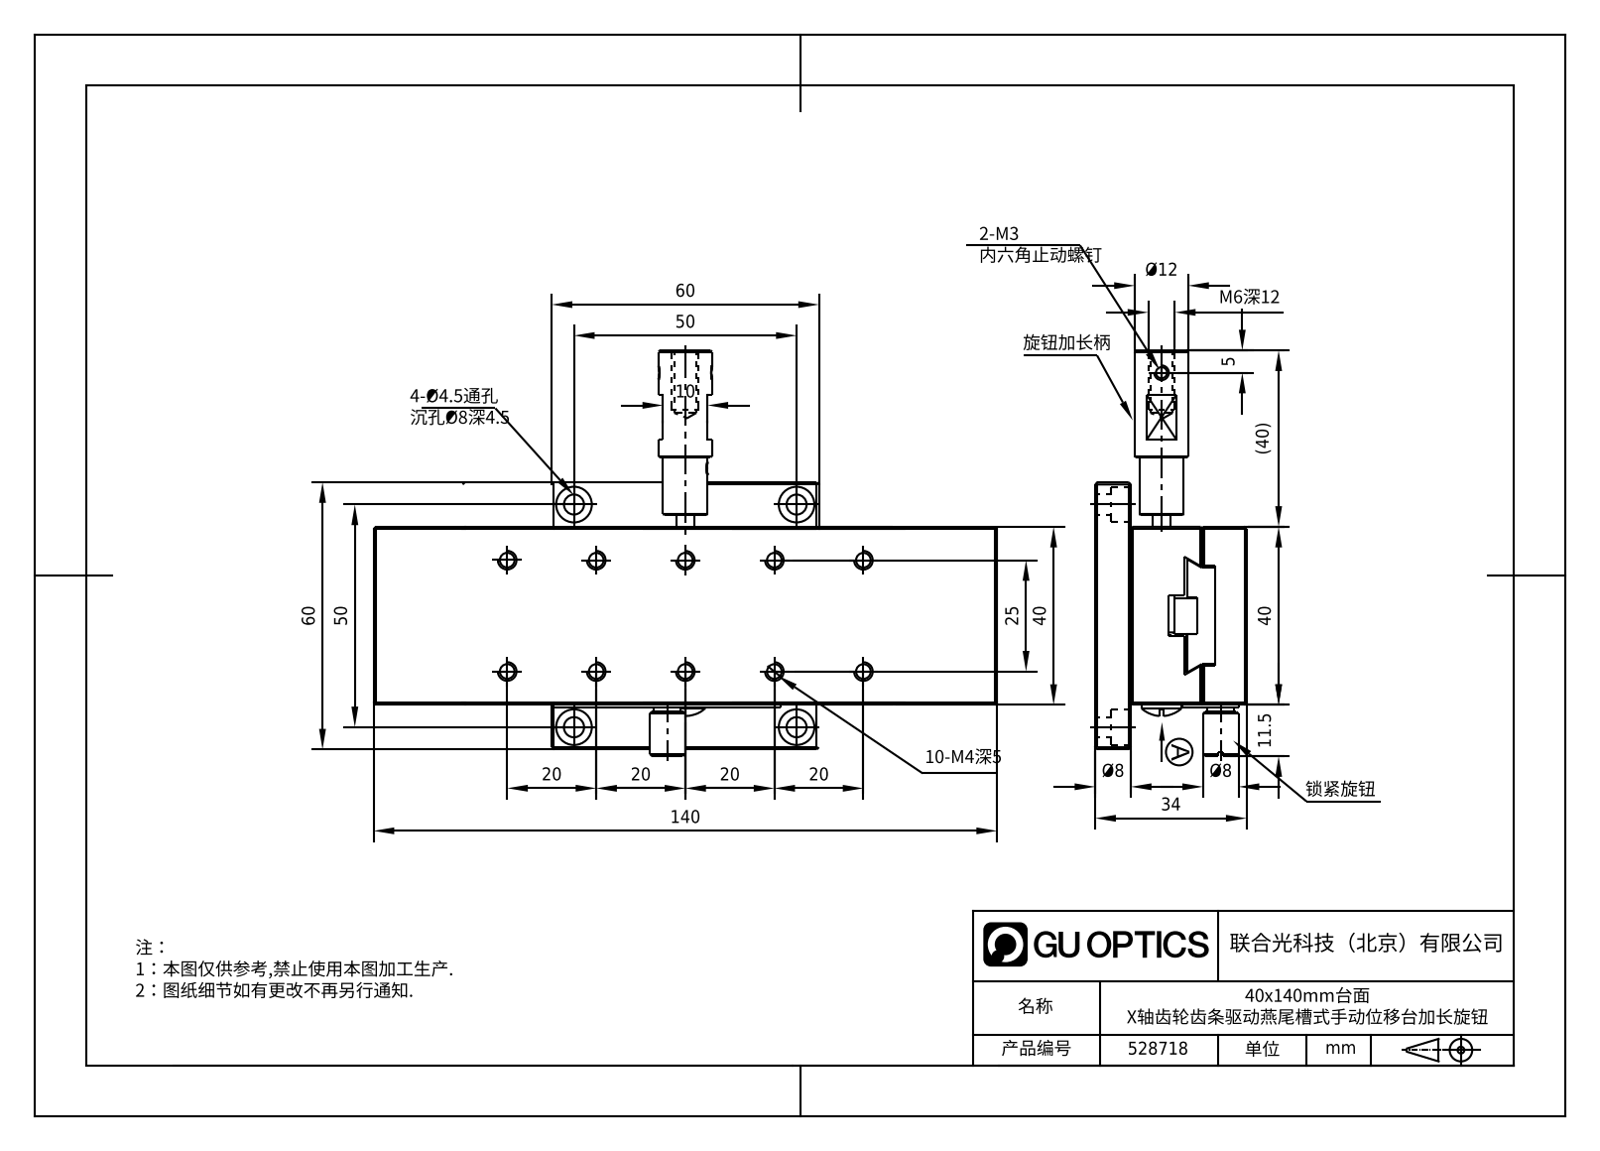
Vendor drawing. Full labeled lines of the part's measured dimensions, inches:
Part name (STEP PRODUCT): 528718
STEP written by: SolidWorks 2020 (CONFIG_CONTROL_DESIGN)
Units: inches
Bodies: 0 solids, 340 faces (190 planar, 80 cylindrical, 70 other)
Overall size (bounding box): 5.512 × 3.602 × 1.339
Round holes (diameter × count): ⌀0.128 ×12, ⌀0.079 ×7, ⌀0.11 ×7, ⌀0.197 ×7, ⌀0.315 ×6, ⌀0.177 ×4, ⌀0.062 ×3, ⌀0.087 ×3, ⌀0.097 ×3, ⌀0.165 ×2, ⌀0.097 ×1, ⌀0.157 ×1
Round bosses / shafts (diameter × count): ⌀0.315 ×2, ⌀0.472 ×1, ⌀0.394 ×1, ⌀0.354 ×1, ⌀0.256 ×1, ⌀0.236 ×1, ⌀0.23 ×1, ⌀0.138 ×1
Partial cylindrical surfaces — rounded edges, fillets, slot ends (radius × count): R0.079 ×4, R0.071 ×2
Main face-to-face distances: 0.276, 0.748, 1.024, 0.63, 0.394, 0.945, 0.02, 1.339, 1.575, 0.118
Hole centre spacings: 0.787, 1.1, 1.261, 1.774, 0.984, 1.575, 1.857, 2.559
